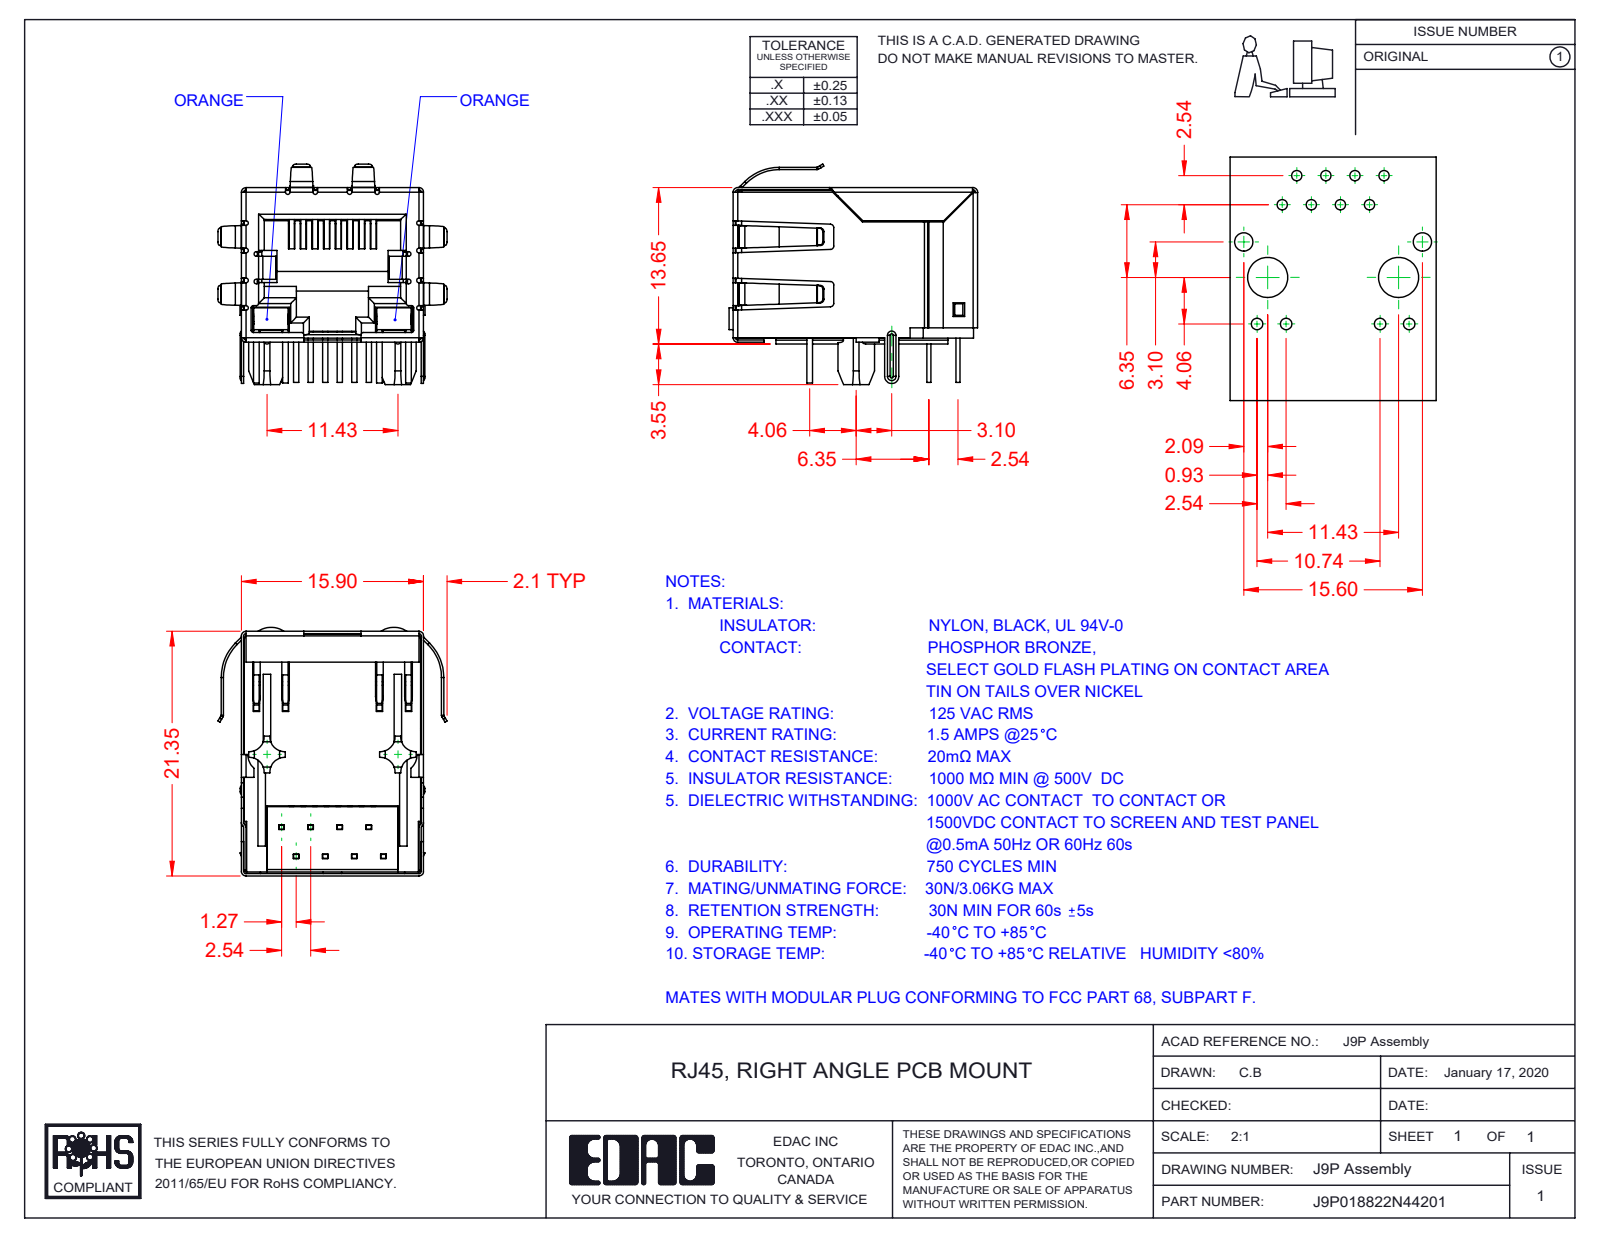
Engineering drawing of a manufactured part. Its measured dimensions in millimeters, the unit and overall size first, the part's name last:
Units: millimetres
Overall size (bounding box): 21.7 × 20 × 19.25
Partial cylindrical surfaces — rounded edges, fillets, slot ends (radius × count): R0.2 ×39, R0.5 ×22, R0.3 ×20, R0.4 ×16, R1.3 ×8, R0.23 ×5, R0.11 ×4, R0.31 ×4
Main face-to-face distances: 15.45, 15.7, 15.65, 0.35, 0.54, 15.5, 12.36, 0.6, 1.4, 0.59
Volume: 2 687 mm³ · Surface area: 7 515 mm²
Bodies: 13 solids, 1472 faces (1042 planar, 336 cylindrical, 94 other)
Part name (STEP PRODUCT): 9P-LED Shield; 9P-LED Contacts; J9P018822N44202; 9P-LED LED RH_4-Orange (+4 more)
STEP written by: SolidWorks 2016 (CONFIG_CONTROL_DESIGN)
